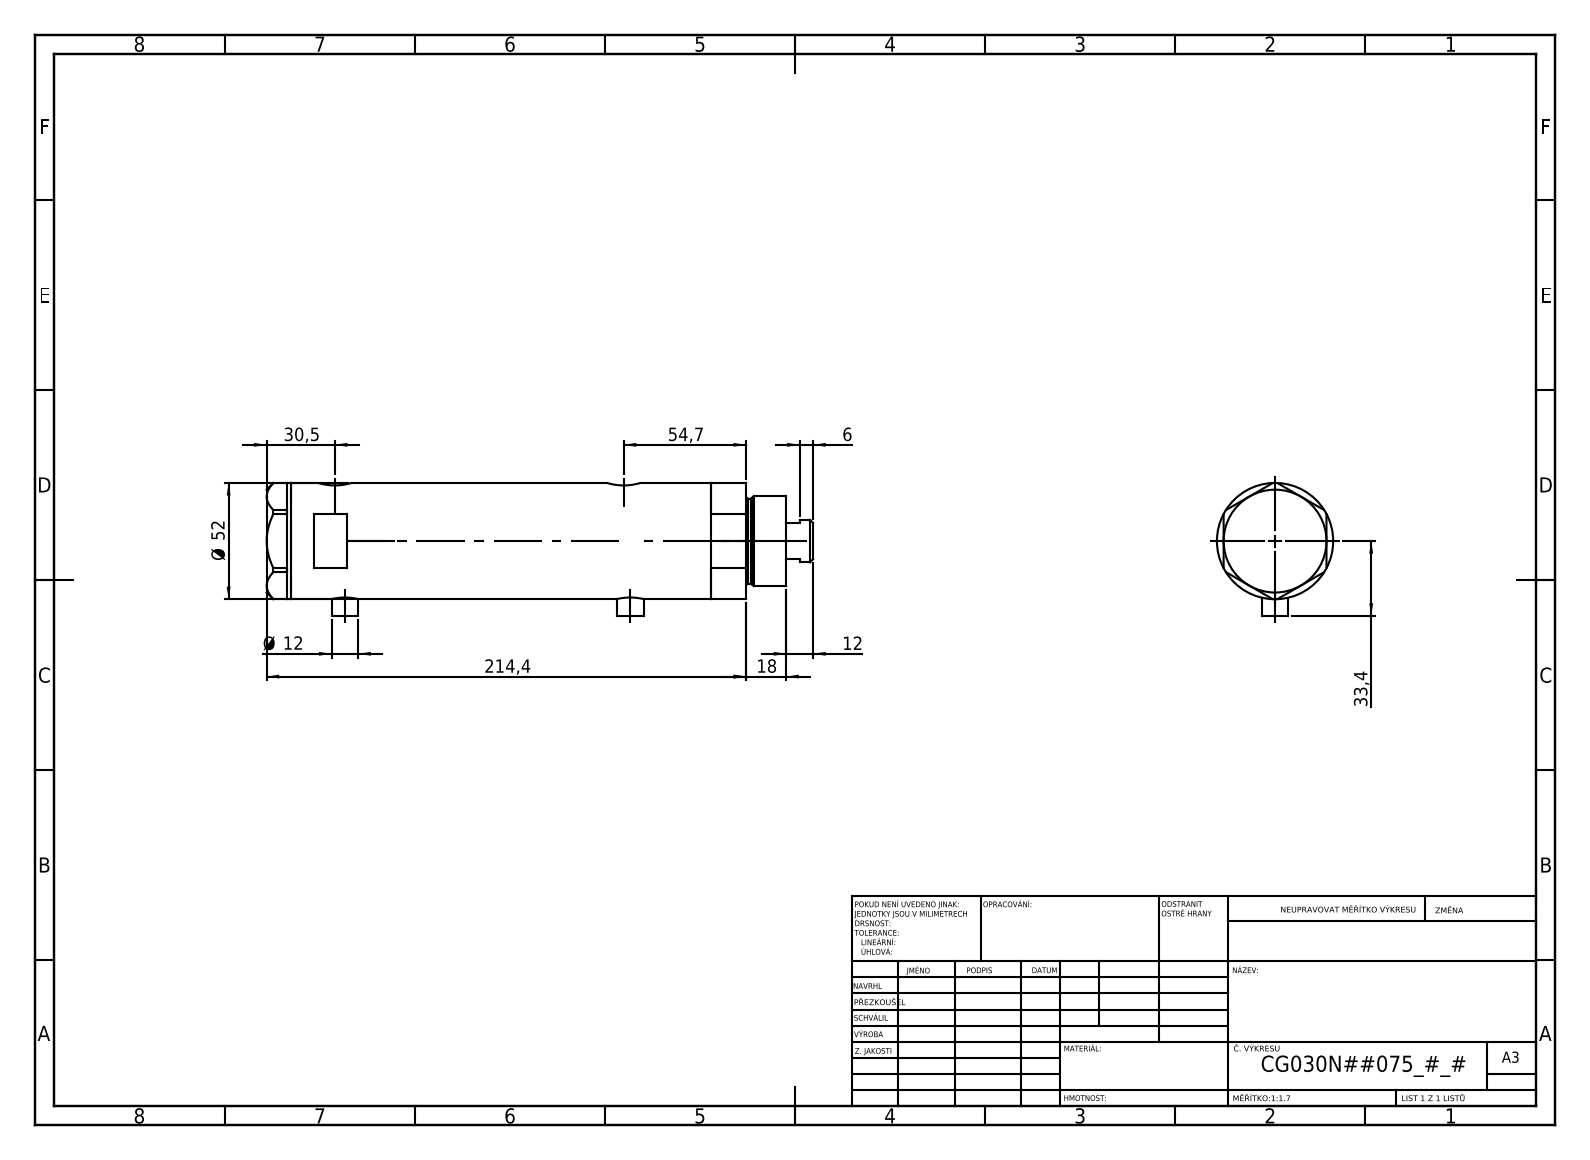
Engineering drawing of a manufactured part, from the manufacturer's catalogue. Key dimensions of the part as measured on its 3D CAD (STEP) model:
Part name (STEP PRODUCT): V270CG_VC; V270CG_MIDDLE; V270CG_BACK; V270CG_FRONT
STEP written by: SolidWorks 2019 (CONFIG_CONTROL_DESIGN)
Units: millimetres
Bodies: 4 solids, 134 faces (65 planar, 49 cylindrical, 20 other)
Overall size (bounding box): 244.4 × 59.4 × 52
Volume: 444 671 mm³ · Surface area: 96 833 mm²
Round holes (diameter × count): ⌀9.73 ×2, ⌀12.5 ×2, ⌀15 ×2, ⌀6.5 ×1, ⌀20 ×1, ⌀21.5 ×1, ⌀30 ×1, ⌀33 ×1, ⌀44 ×1
Round bosses / shafts (diameter × count): ⌀12 ×2, ⌀52 ×1, ⌀40 ×1, ⌀38 ×1, ⌀19 ×1
Main face-to-face distances: 151.5, 23.8, 127.7, 11, 34.8, 162.5, 46, 198.9, 187.9, 164.1
Hole centre spacings: 2.9, 4.5, 124.7, 127.6, 129.2, 132.1
